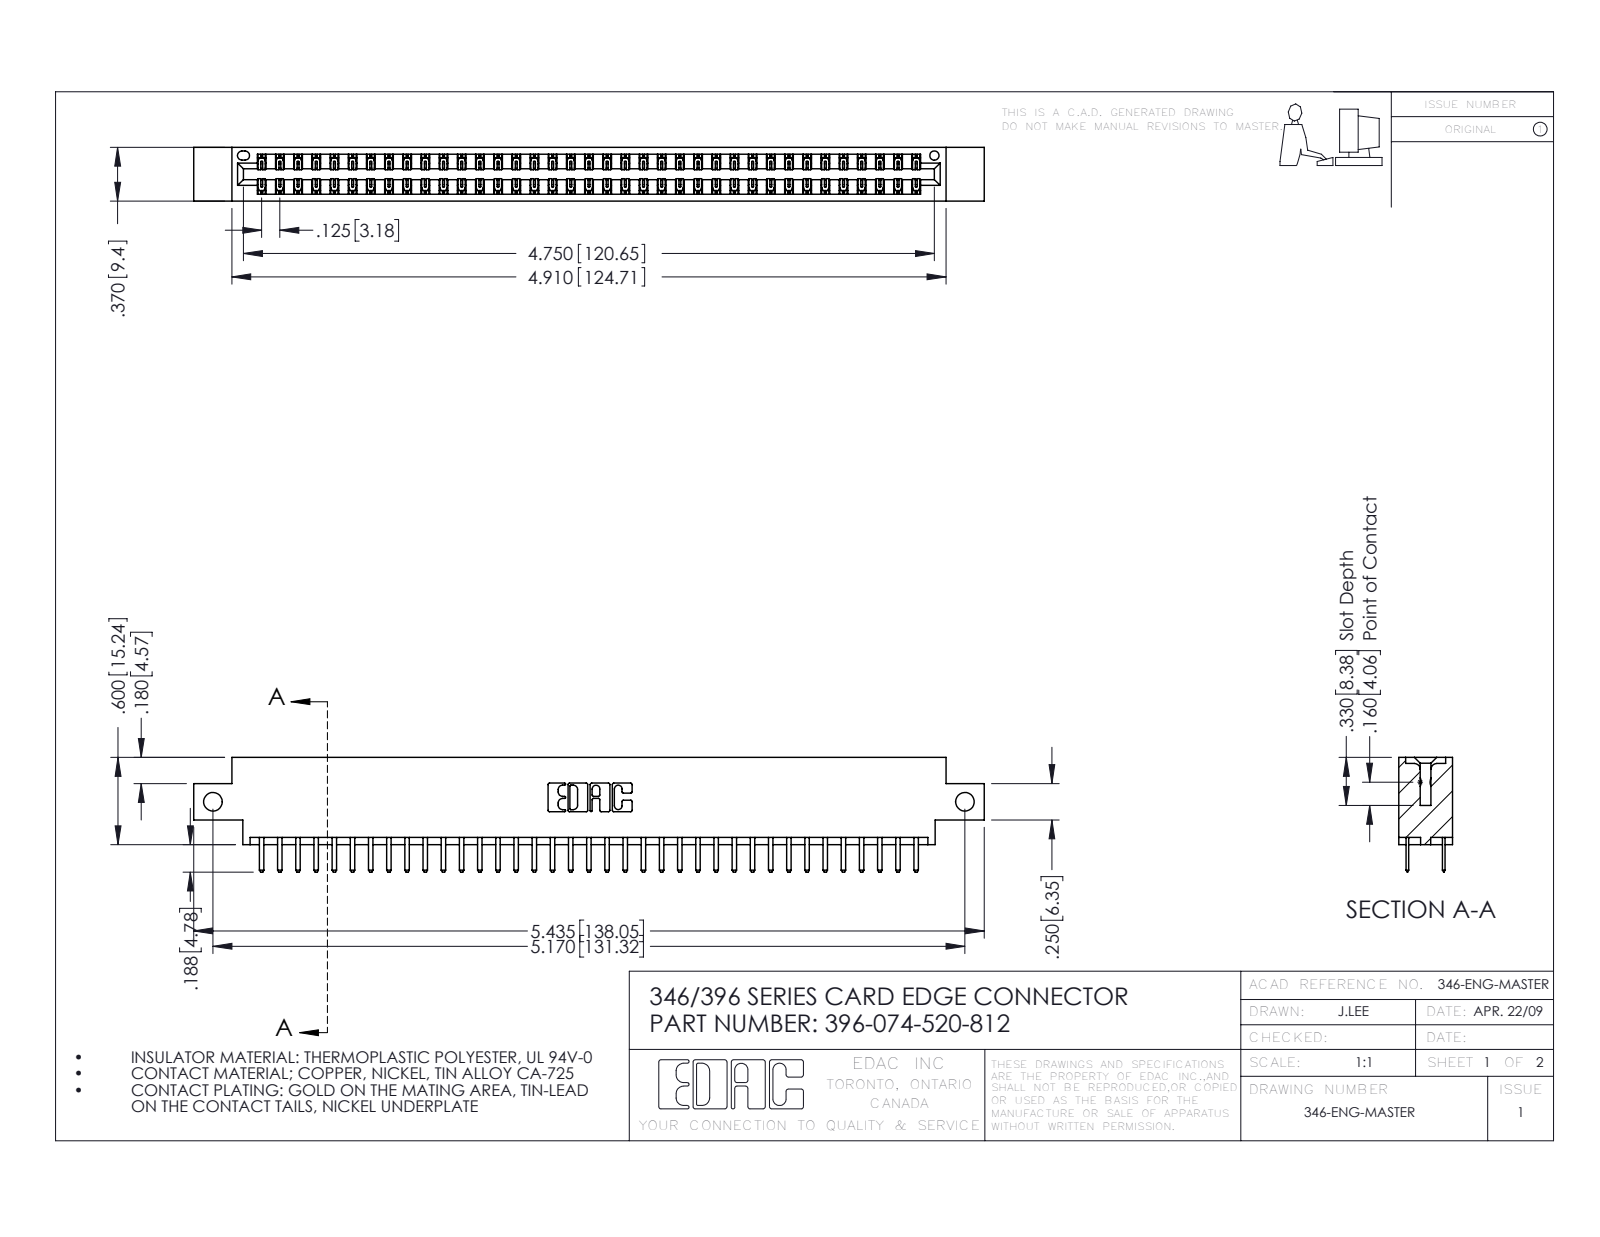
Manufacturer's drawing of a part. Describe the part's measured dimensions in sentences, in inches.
The part is named "345-292-001_345-293-120; 396-074-520-812; 346 Part_0.170 Offset - Side Mount". Its 3-D file was written by "SolidWorks 2016 (CONFIG_CONTROL_DESIGN)". It is 75 solids with 4270 faces: 2818 planar, 1452 cylindrical and 0 other. Overall it measures 5.435 by 0.788 by 0.37 inches. Its volume is 0.802 cubic inches and its surface area 27.84 square inches. Round holes: 2 of diameter 0.128, 1 of diameter 0.064. Partial cylindrical surfaces (rounded edges, fillets, slot ends): 111 of radius 0.006, 78 of radius 0.01, 22 of radius 0.01, 6 of radius 0.007, 6 of radius 0.031, 3 of radius 0.026, 2 of radius 0.014, 2 of radius 0.022. The main face-to-face distances are 0.048, 0.322, 0.37, 0.25, 0.275, 0.072, 0.298, 0.025, 0.148, 0.222. The hole center spacings are 5.17.
